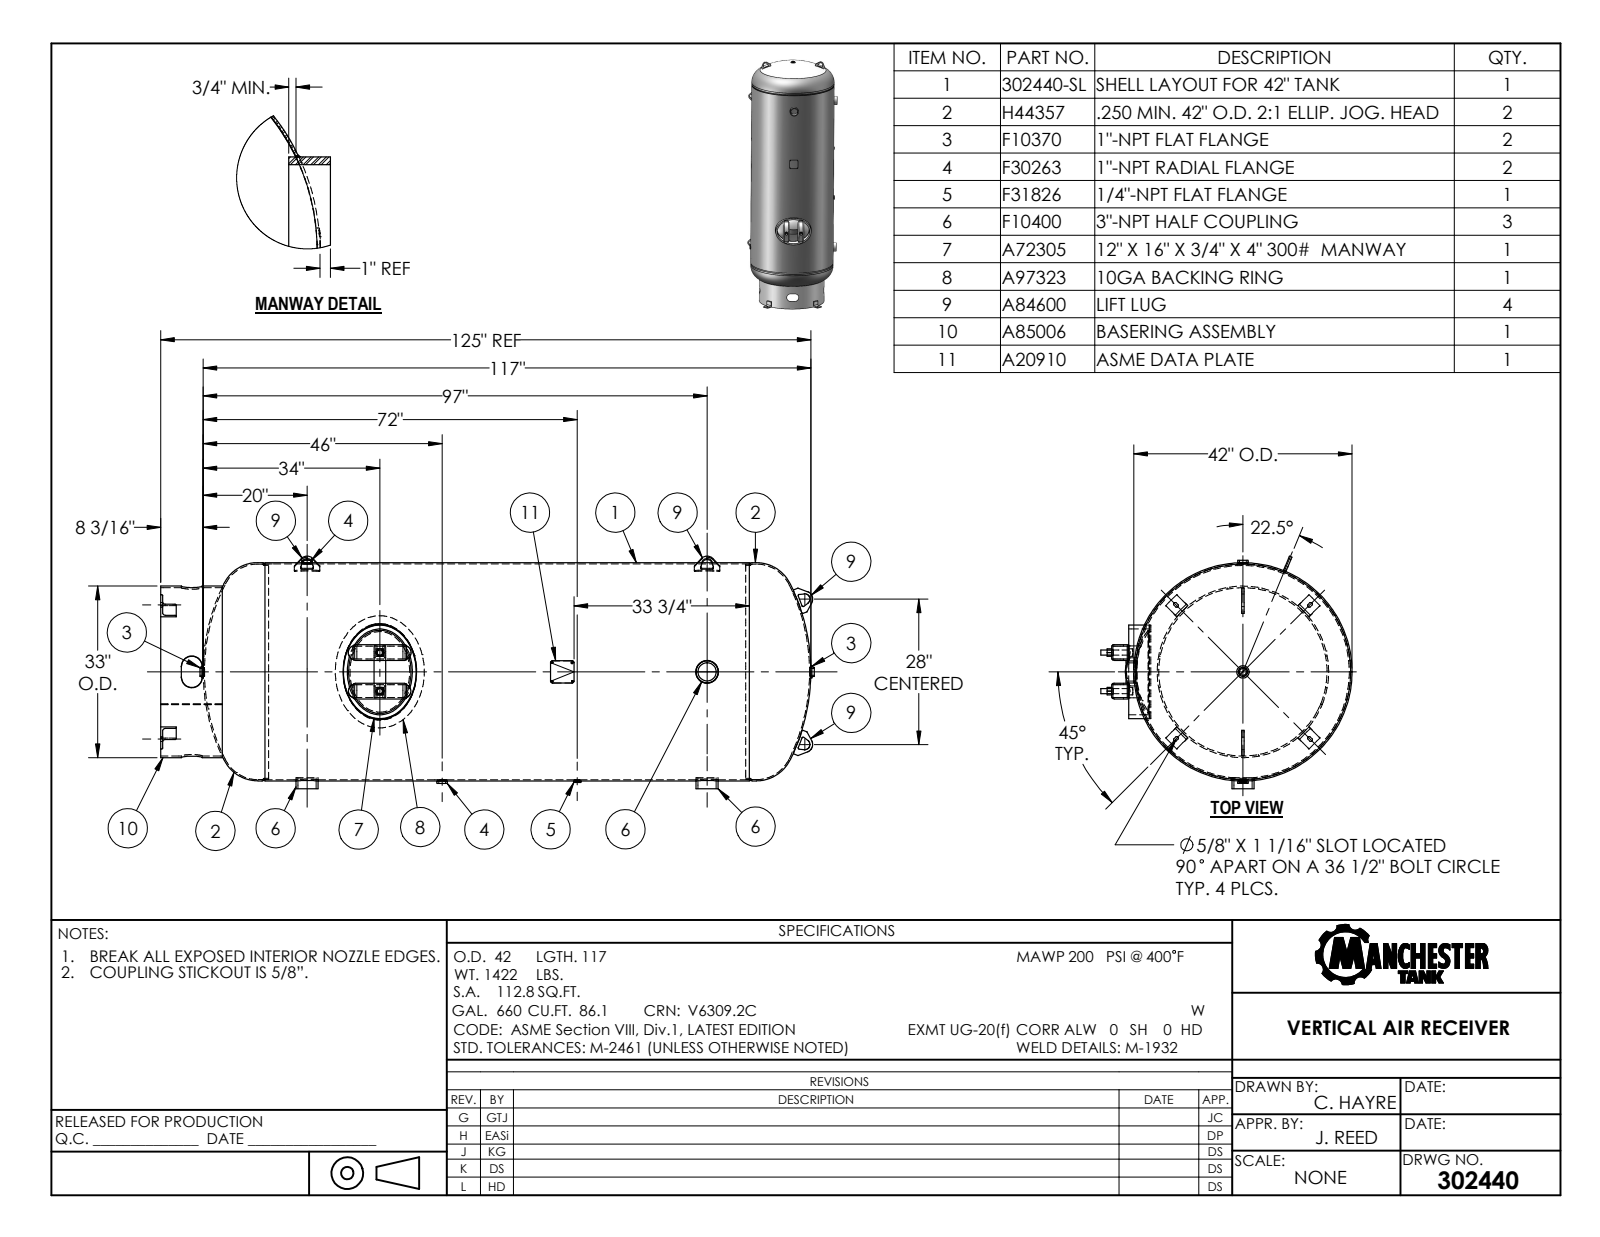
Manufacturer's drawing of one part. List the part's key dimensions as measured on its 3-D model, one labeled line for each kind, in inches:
Part name (STEP PRODUCT): 302440
STEP written by: SolidWorks 2011 (CONFIG_CONTROL_DESIGN)
Units: inches
Bodies: 0 solids, 322 faces (129 planar, 110 cylindrical, 83 other)
Overall size (bounding box): 126.69 × 48.371 × 43.57
Round holes (diameter × count): ⌀3.5 ×3, ⌀1.315 ×2, ⌀1.375 ×2, ⌀1.375 ×2, ⌀0.54 ×1, ⌀1.315 ×1, ⌀32.376 ×1
Round bosses / shafts (diameter × count): ⌀4.25 ×3, ⌀2.375 ×3, ⌀1 ×2, ⌀42 ×1, ⌀41.5 ×1, ⌀33 ×1, ⌀1.75 ×1, ⌀1.5 ×1
Partial cylindrical surfaces — rounded edges, fillets, slot ends (radius × count): R0.255 ×8, R0.312 ×6, R0.375 ×4, R0.562 ×4, R1.318 ×4, R2 ×4, R0.313 ×2, R0.188 ×1
Main face-to-face distances: 0.25, 0.5, 4, 4.25, 21.75, 113.358, 93.25, 20.109, 3, 2.211
Hole centre spacings: 23.97, 26, 77, 25, 28, 51, 52
